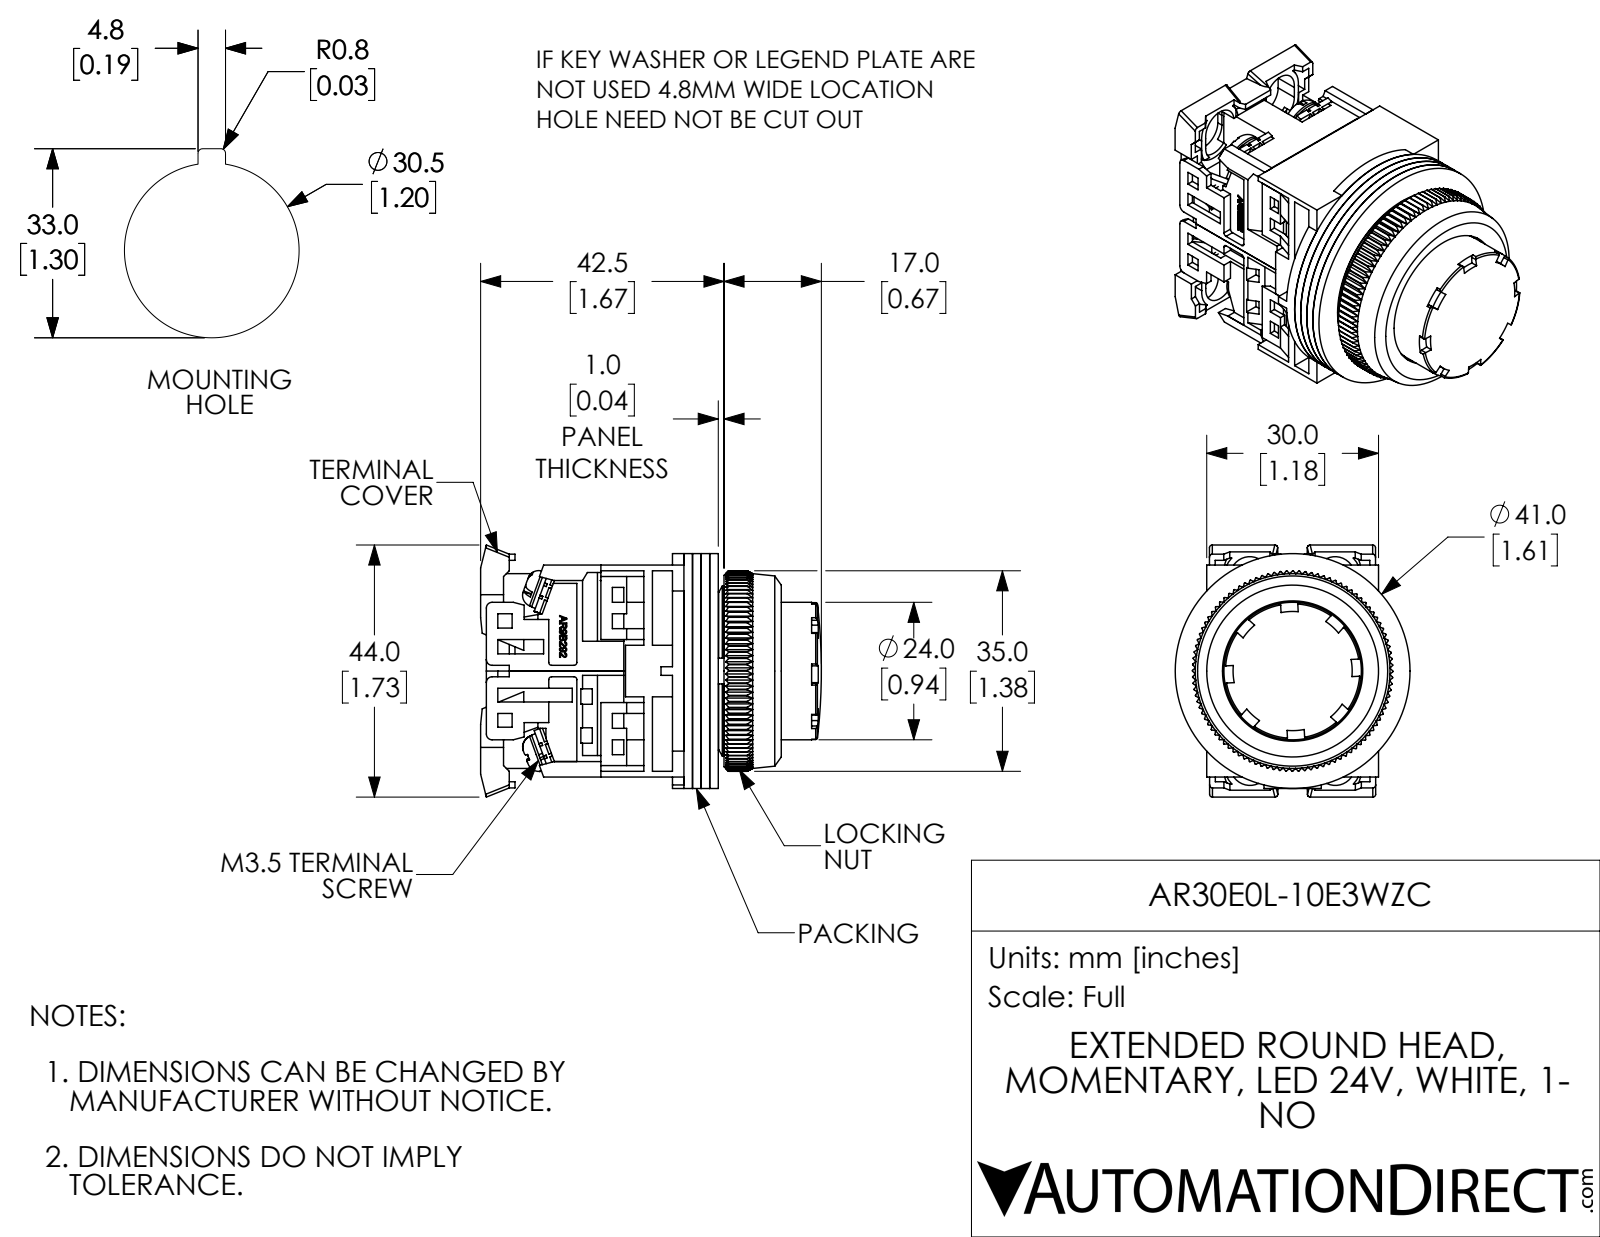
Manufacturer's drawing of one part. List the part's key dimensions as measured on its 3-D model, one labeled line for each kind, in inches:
Part name (STEP PRODUCT): AR30E0L-10E3WZC
STEP written by: SolidWorks 2017 (AUTOMOTIVE_DESIGN)
Units: inches
Bodies: 25 solids, 2022 faces (1378 planar, 323 cylindrical, 321 other)
Overall size (bounding box): 2.343 × 1.732 × 1.614
Volume: 2.119 in³ · Surface area: 59.85 in²
Round holes (diameter × count): ⌀0.138 ×8, ⌀0.142 ×4, ⌀0.118 ×1, ⌀0.472 ×1, ⌀0.709 ×1, ⌀0.728 ×1, ⌀0.787 ×1, ⌀0.945 ×1, ⌀0.965 ×1, ⌀1.122 ×1, ⌀1.252 ×1
Round bosses / shafts (diameter × count): ⌀0.26 ×4, ⌀0.138 ×4, ⌀1.614 ×1, ⌀1.181 ×1, ⌀0.866 ×1, ⌀0.776 ×1, ⌀0.551 ×1
Partial cylindrical surfaces — rounded edges, fillets, slot ends (radius × count): R0.012 ×16, R0.059 ×16, R0.02 ×12, R0.039 ×4, R0.138 ×4, R0.177 ×4, R0.118 ×2, R0.398 ×1
Main face-to-face distances: 0.059, 0.118, 0.039, 0.177, 0.811, 1.417, 0.634, 0.079, 1.358, 0.689
Hole centre spacings: 0.579, 0.61
